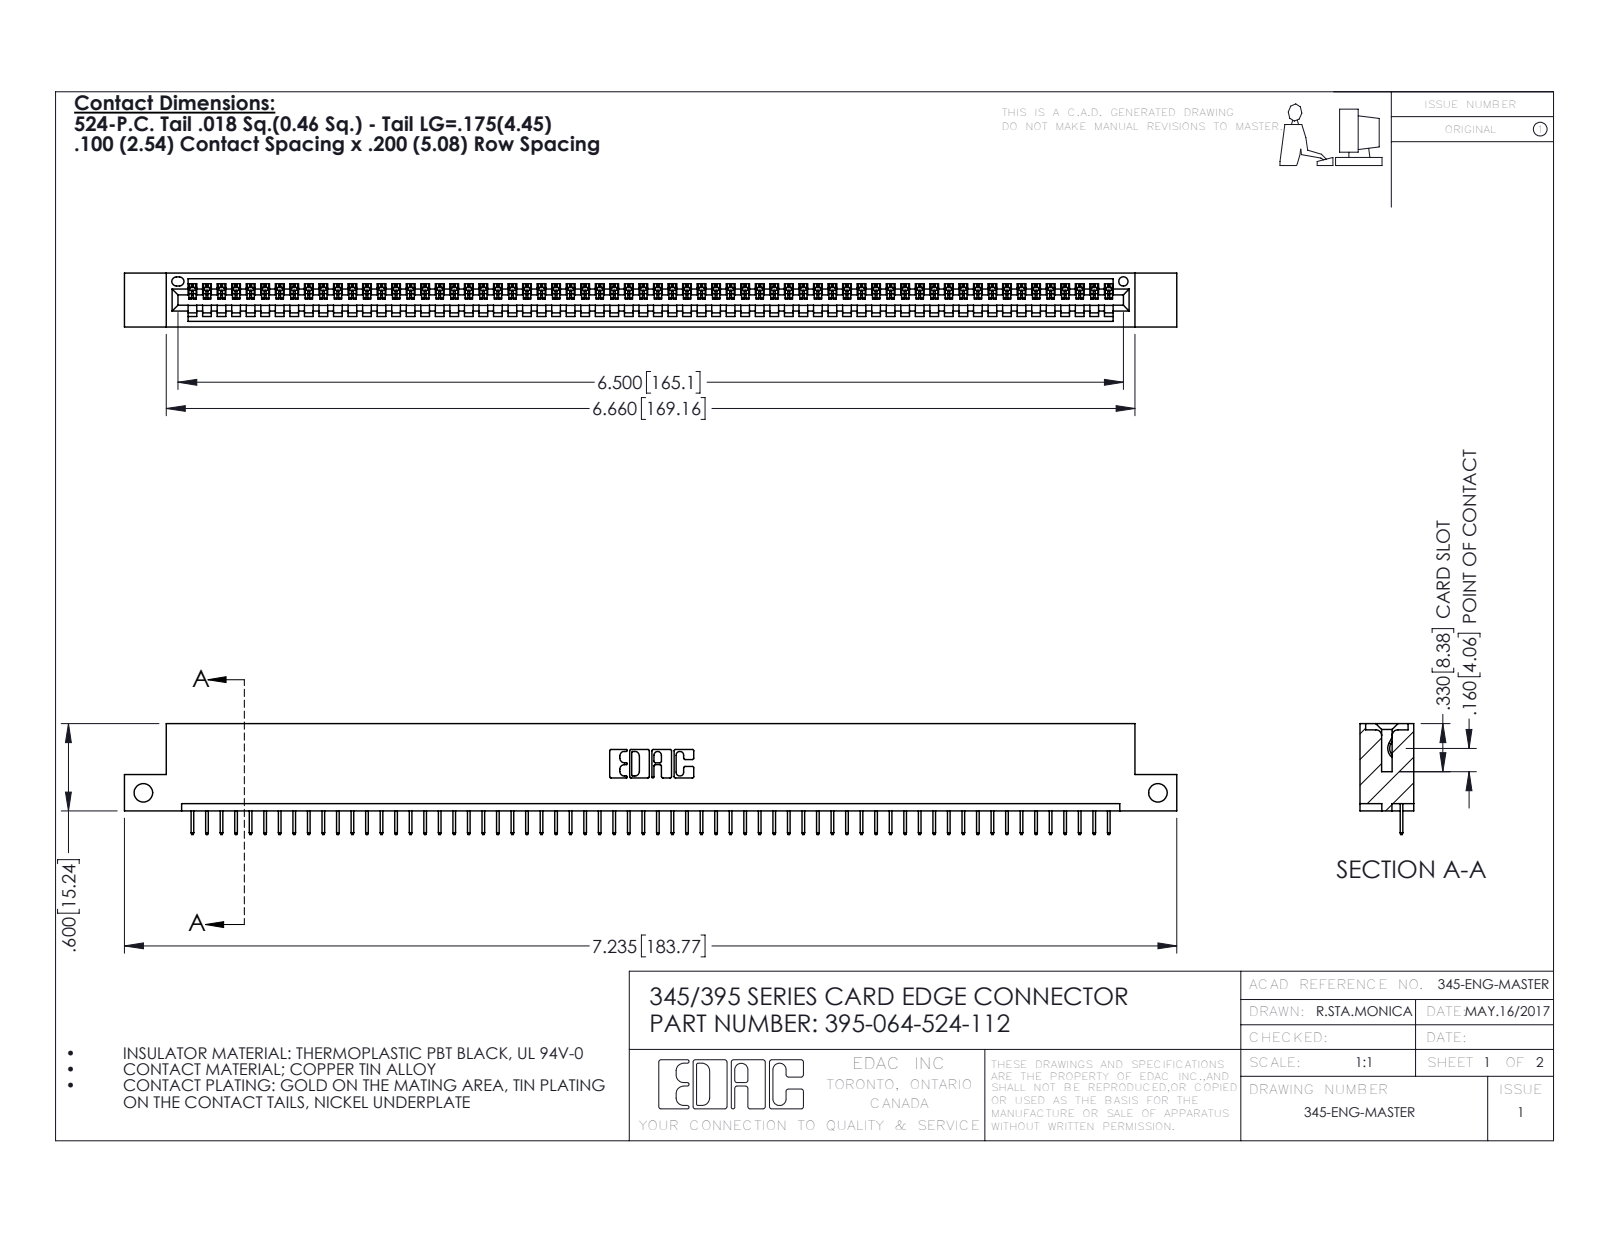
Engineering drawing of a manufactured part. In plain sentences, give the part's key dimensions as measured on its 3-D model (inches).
The part is named "345-292-001_345-293-124; 395-064-524-112; 345 Part_Flush Mounting Lugs - Side Mount". Its 3-D file was written by "SolidWorks 2016 (CONFIG_CONTROL_DESIGN)". It is 65 solids with 4094 faces: 3024 planar, 1070 cylindrical and 0 other. Overall it measures 7.235 by 0.762 by 0.37 inches. Its volume is 1.055 cubic inches and its surface area 34.61 square inches. Round holes: 2 of diameter 0.128, 1 of diameter 0.064. Partial cylindrical surfaces (rounded edges, fillets, slot ends): 128 of radius 0.006, 22 of radius 0.01, 6 of radius 0.007, 6 of radius 0.031, 3 of radius 0.026, 2 of radius 0.031, 2 of radius 0.04, 1 of radius 0.014. The main face-to-face distances are 0.298, 0.072, 0.37, 0.2, 0.098, 0.272, 0.025, 0.225, 0.072, 0.149. The hole center spacings are 6.975.
